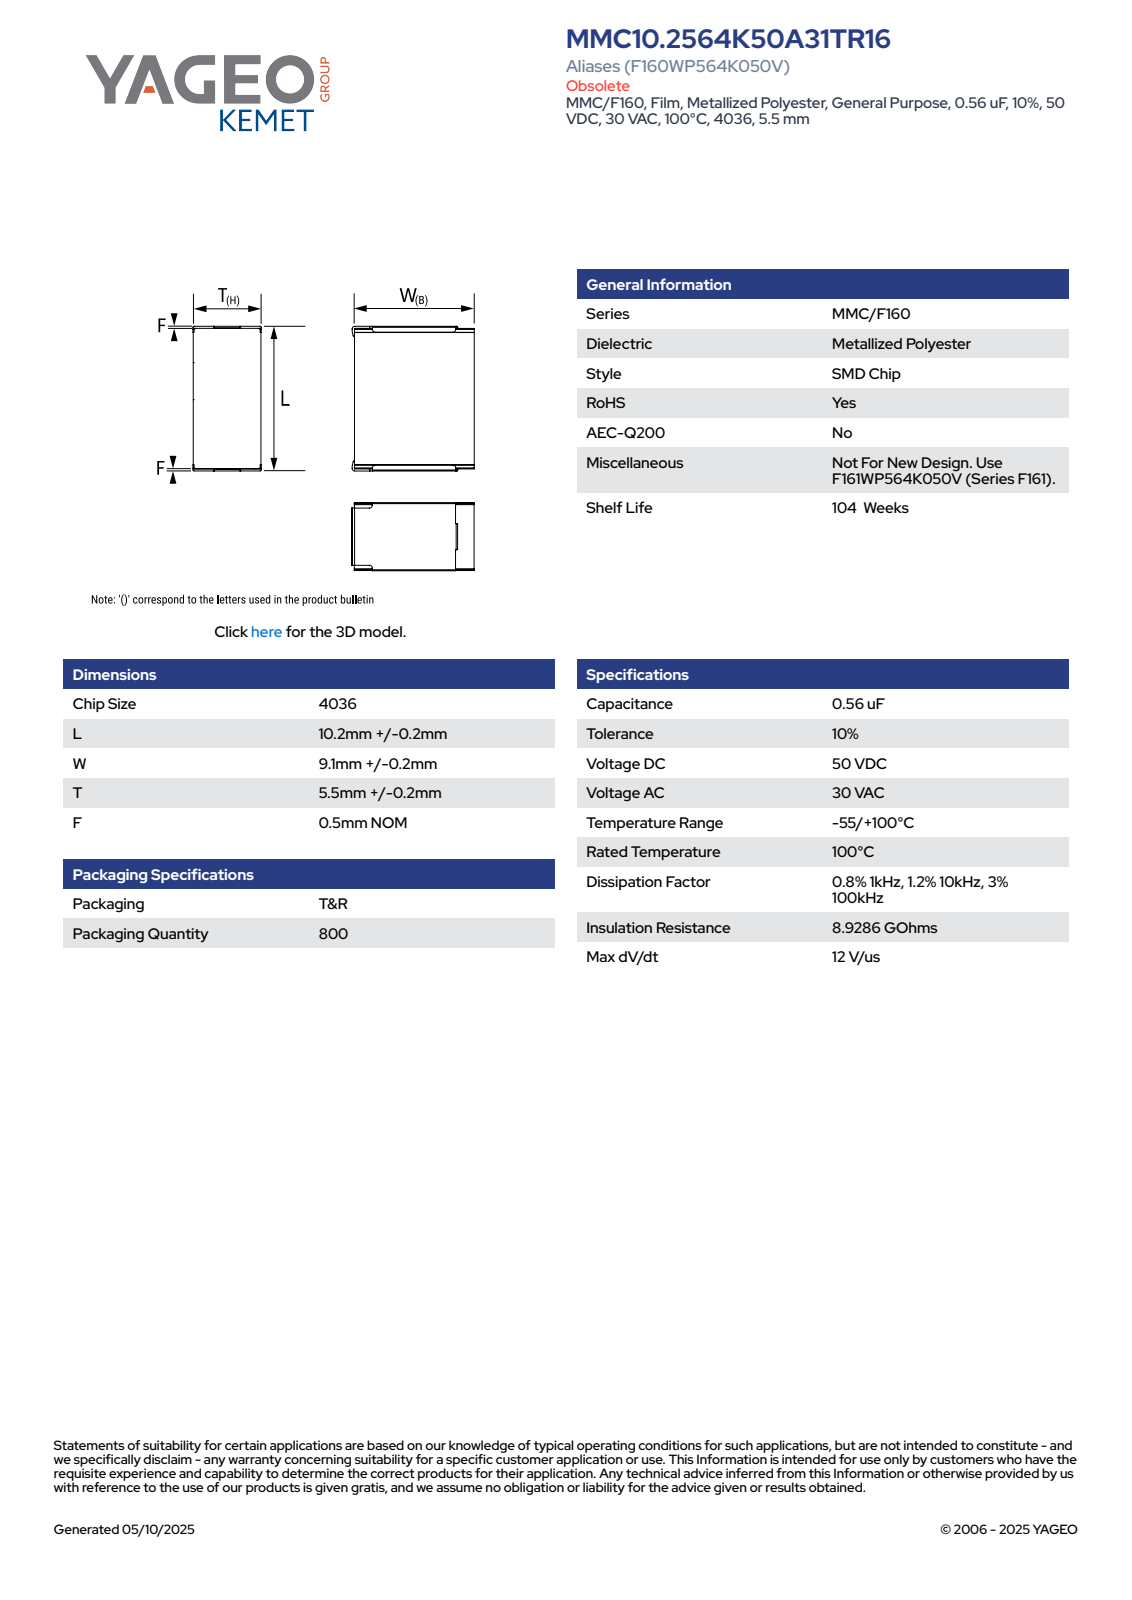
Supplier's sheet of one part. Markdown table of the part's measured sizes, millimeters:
| quantity | value |
| --- | --- |
| part name | CFS_KSTD_4036_L10.40W9.30T5.7F0.5 |
| STEP written by | SolidWorks 2021 (AUTOMOTIVE_DESIGN) |
| units | millimeters |
| bodies | 4 solids, 117 faces (103 planar, 14 cylindrical, 0 other) |
| overall size | 10.4 × 9.61 × 5.99 |
| volume | 530 mm³ |
| surface area | 440 mm² |
| partial cylindrical surfaces (radius × count) | 0.34 × 10, 0.36 × 4 |
| main face-to-face distances | 5.7, 8.93, 10.4, 0.5, 9.9, 5.85, 9.4, 0.37, 0.68, 0.31 |
